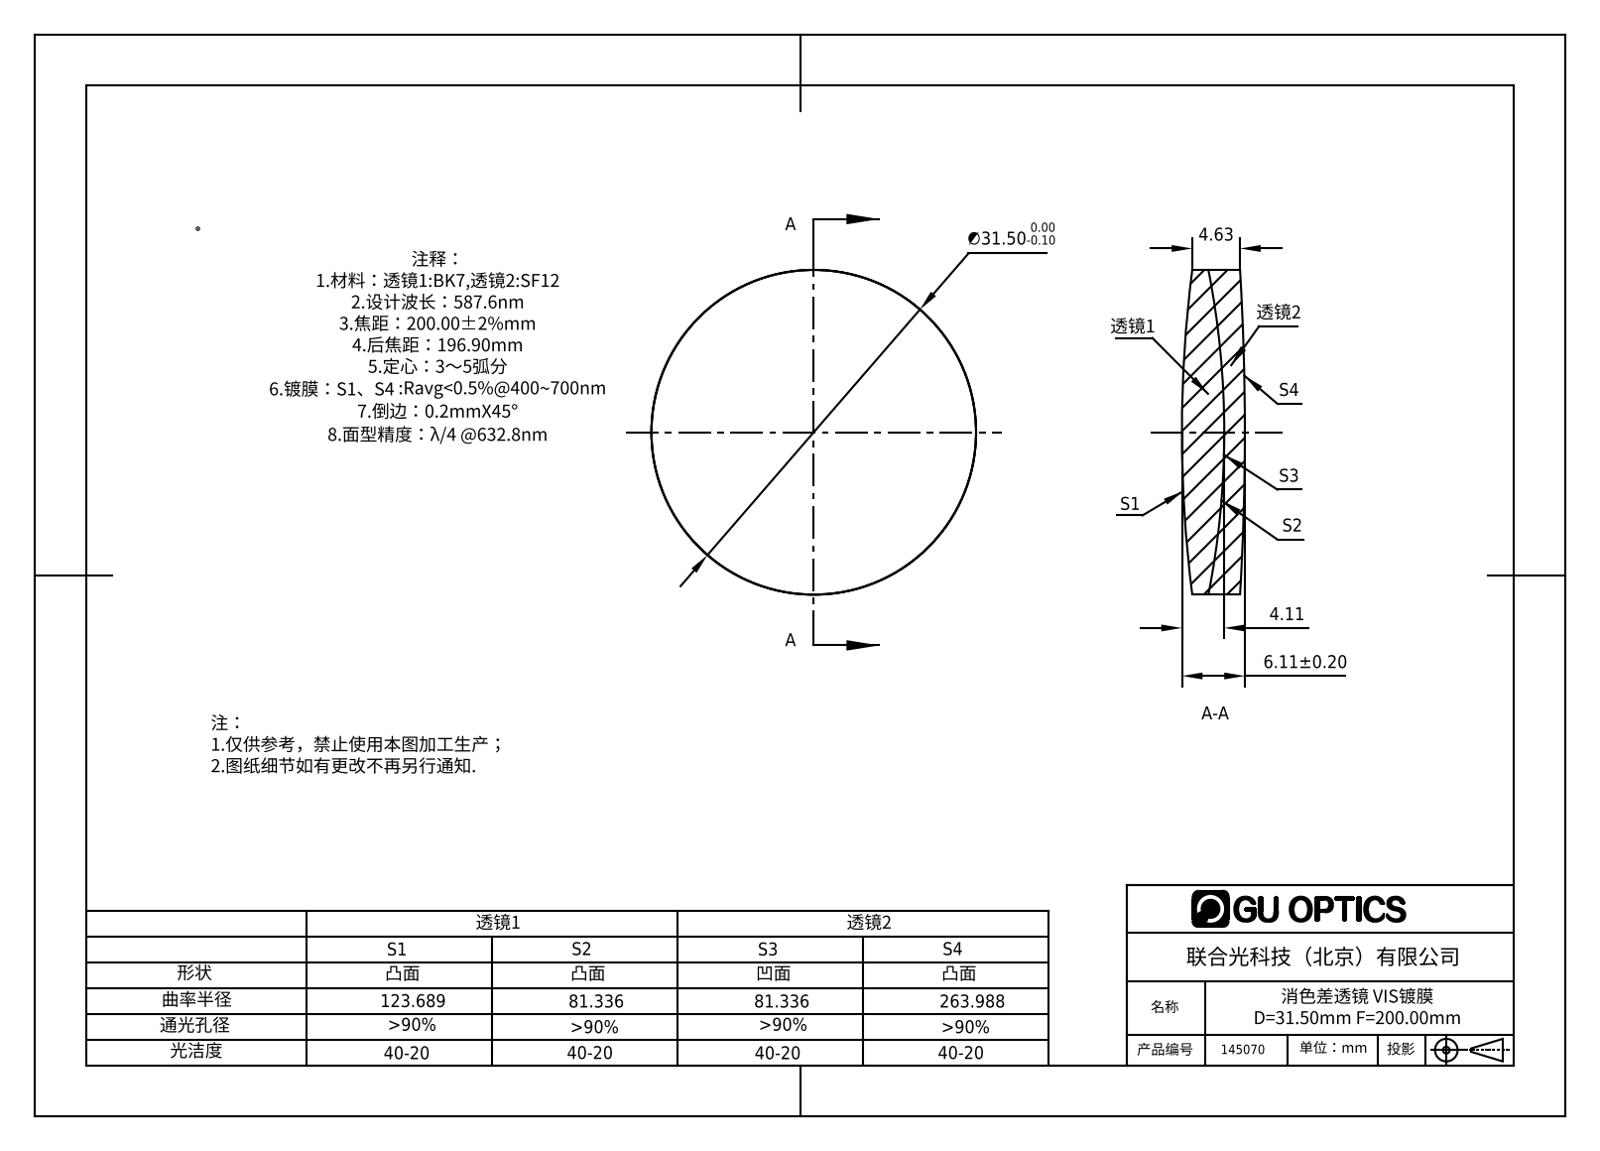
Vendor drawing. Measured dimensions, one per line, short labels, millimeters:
name: 145070
written by: SolidWorks 2016 (AUTOMOTIVE_DESIGN)
unit: mm
bodies: 2 solids, 12 faces (0 planar, 4 cylindrical, 8 other)
size: 31.5 × 31.5 × 6.11
volume: 4 187 mm³; area: 3 594 mm²
bosses: 1× ⌀31.5
